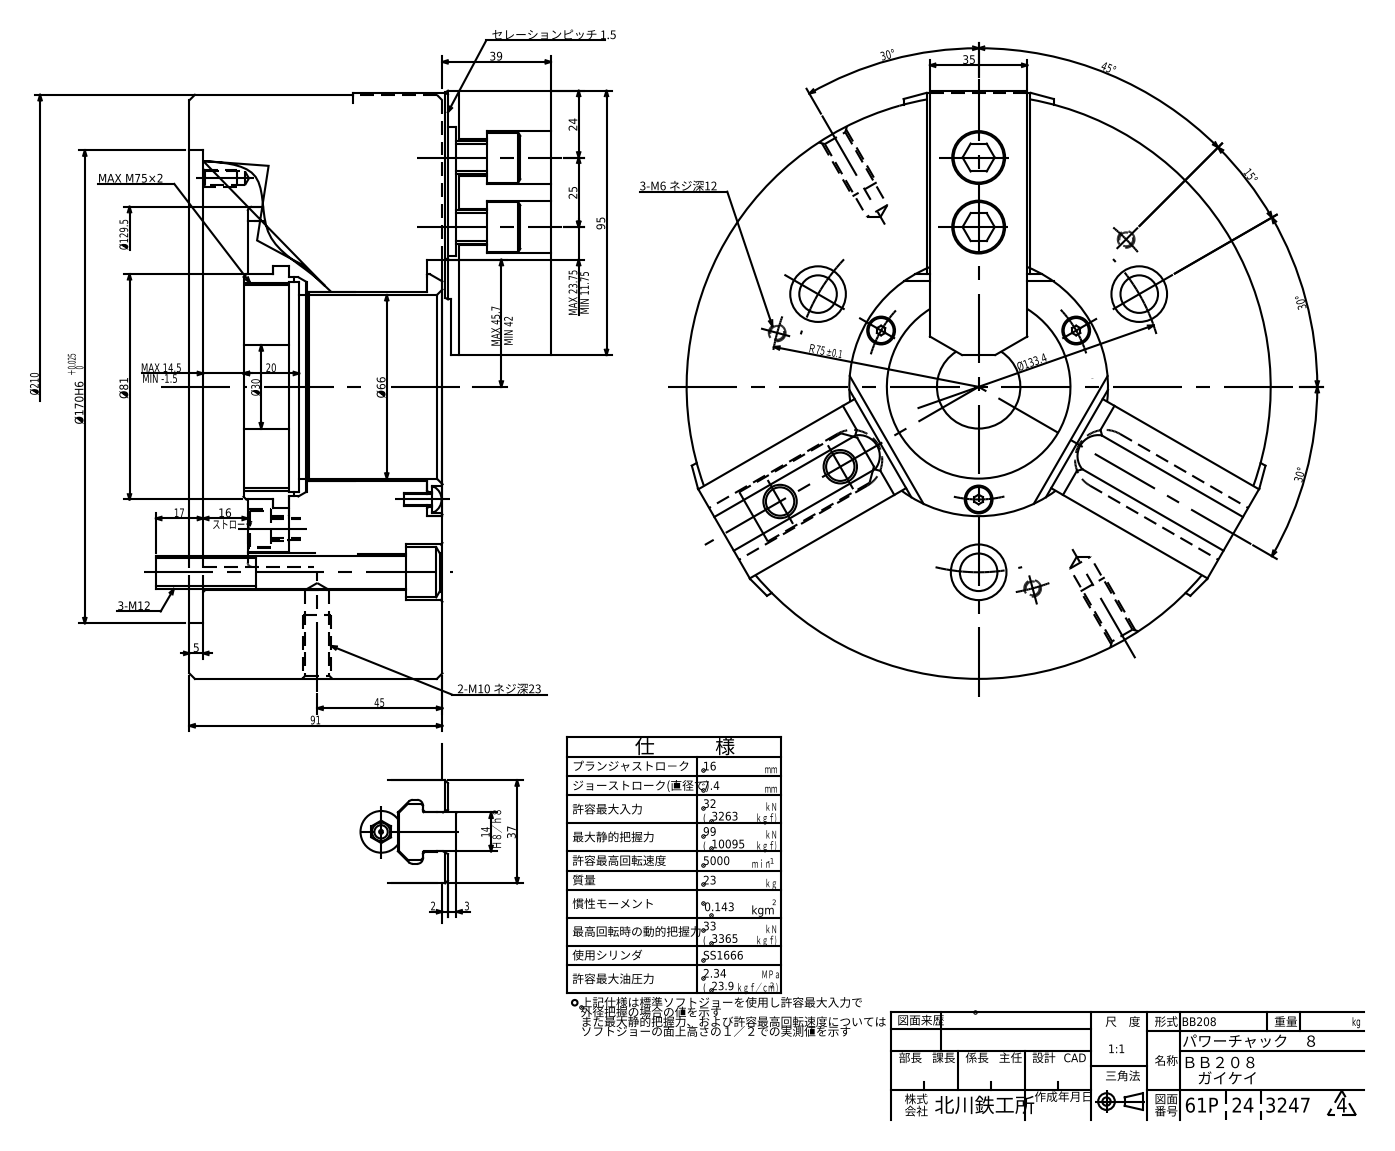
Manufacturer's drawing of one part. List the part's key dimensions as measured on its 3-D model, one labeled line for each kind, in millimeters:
Part name (STEP PRODUCT): BB208
STEP written by: ST-DEVELOPER v16.7 (AUTOMOTIVE_DESIGN)
Units: millimetres
Bodies: 1 solid, 1986 faces (1405 planar, 271 cylindrical, 310 other)
Overall size (bounding box): 211.21 × 210 × 93
Volume: 2 432 000 mm³ · Surface area: 273 284 mm²
Round holes (diameter × count): ⌀3.8 ×12, ⌀6 ×7, ⌀4.92 ×6, ⌀8 ×6, ⌀9 ×6, ⌀14 ×6, ⌀6.65 ×5, ⌀5 ×4, ⌀10 ×4, ⌀2 ×3, ⌀3 ×3, ⌀4.13 ×3
Round bosses / shafts (diameter × count): ⌀210 ×1, ⌀118.7 ×1, ⌀86.9 ×1, ⌀78.8 ×1, ⌀68 ×1
Partial cylindrical surfaces — rounded edges, fillets, slot ends (radius × count): R2 ×18, R5 ×12, R0.4 ×6, R1 ×6, R1.2 ×6, R6 ×6, R6.5 ×6, R7 ×6
Main face-to-face distances: 5, 91, 16.5, 86, 15.1, 0.5, 16, 20.5, 32, 21.5
Hole centre spacings: 15.84, 21.85, 51, 72.87, 76.84, 88.33, 93.84, 102.09
